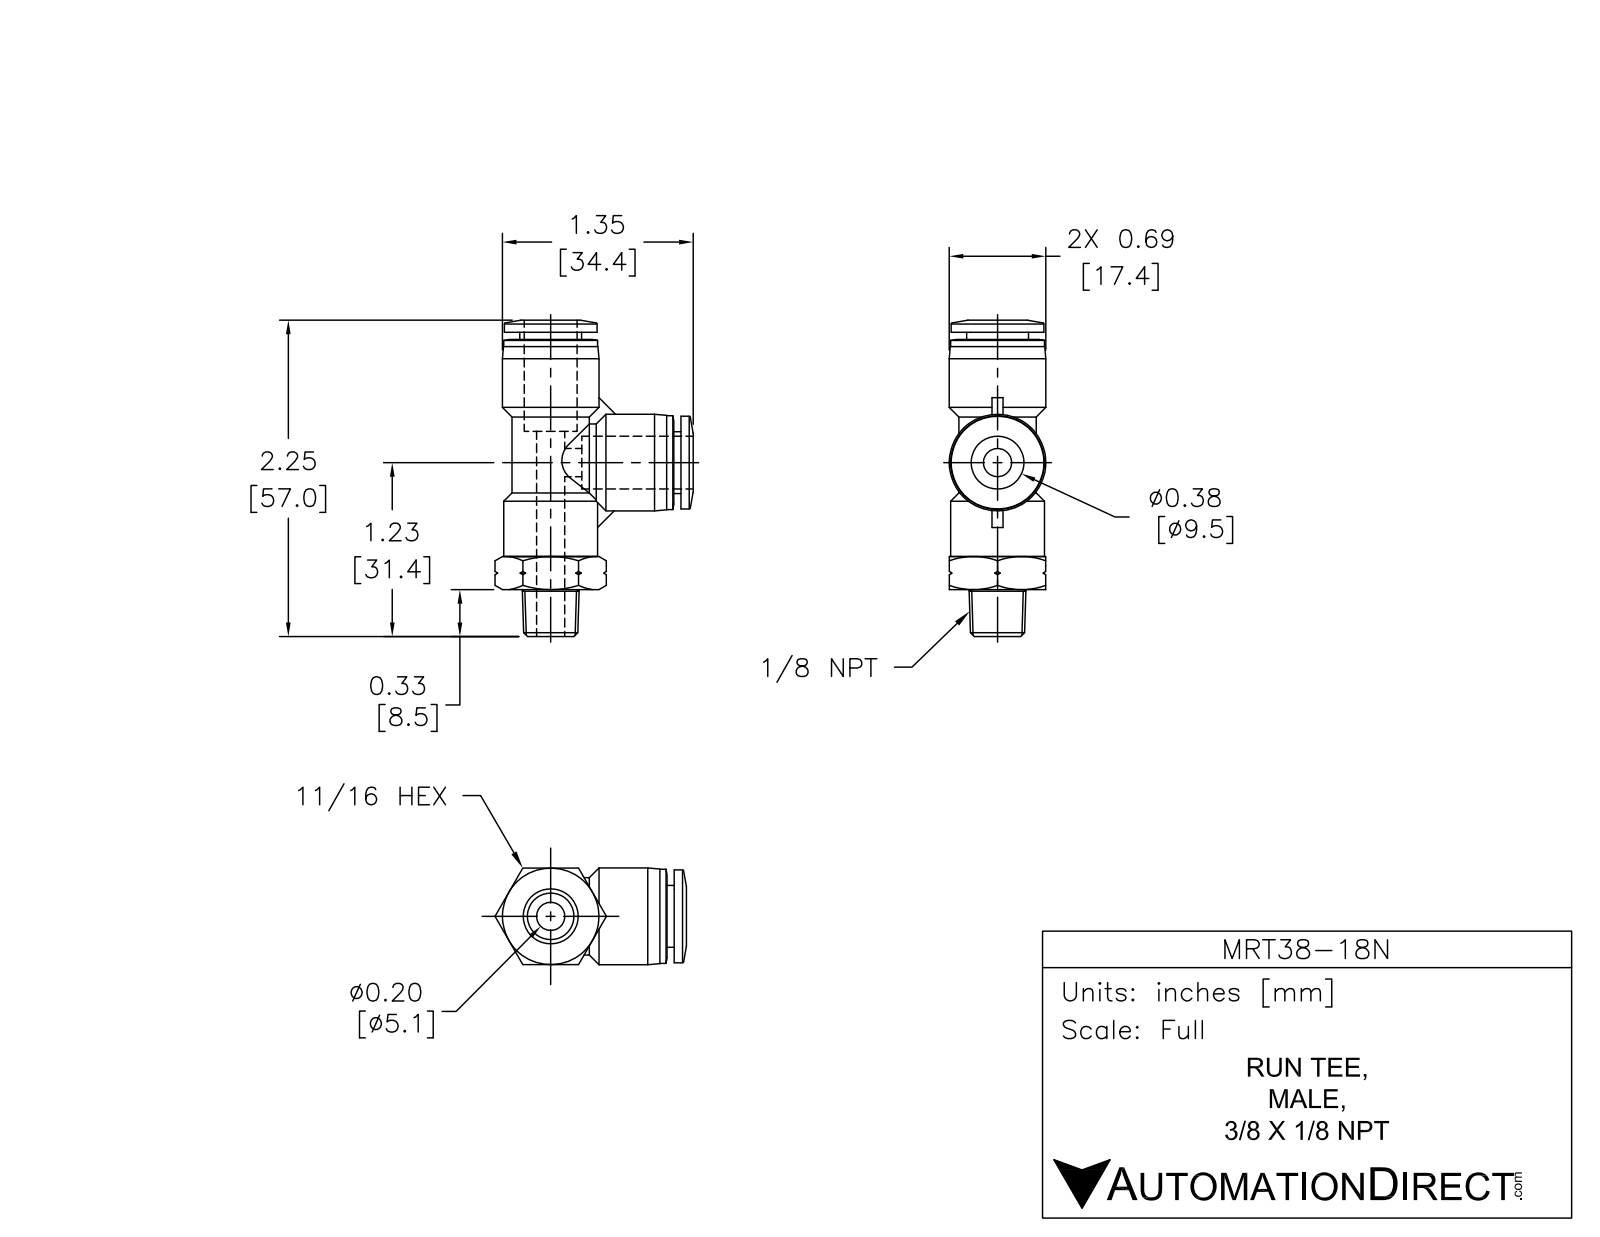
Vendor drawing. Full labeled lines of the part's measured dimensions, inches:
Part name (STEP PRODUCT): MRT38-18N
STEP written by: SolidWorks 2015 (AUTOMOTIVE_DESIGN)
Units: inches
Bodies: 1 solid, 120 faces (24 planar, 30 cylindrical, 66 other)
Overall size (bounding box): 2.256 × 1.413 × 0.689
Volume: 0.659 in³ · Surface area: 10.48 in²
Round holes (diameter × count): ⌀0.236 ×2, ⌀0.386 ×2
Round bosses / shafts (diameter × count): ⌀0.689 ×2, ⌀0.669 ×2, ⌀0.661 ×2, ⌀0.551 ×2, ⌀0.441 ×2
Main face-to-face distances: 0.687, 0.051, 1.835, 0.654, 0.705, 1.783, 1.13, 0.304, 0.383, 0.335
